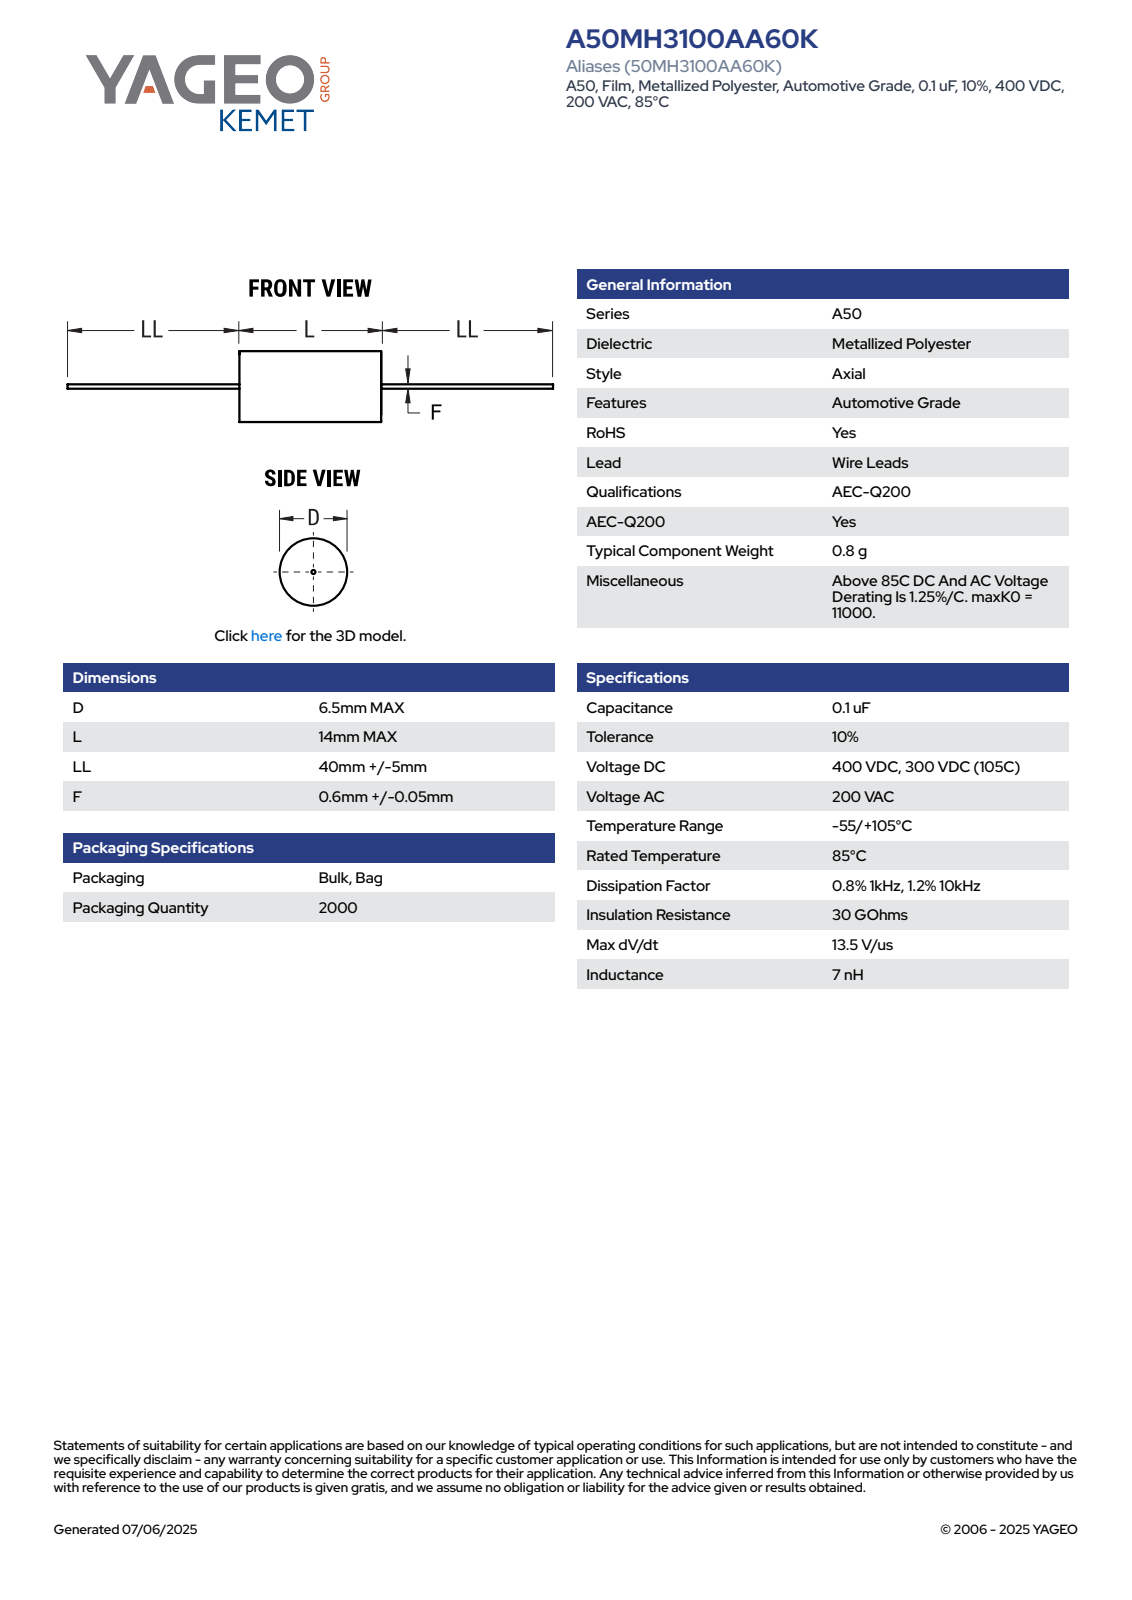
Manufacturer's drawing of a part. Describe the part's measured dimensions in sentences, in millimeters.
The part is named "CFA_ACWF_6.5X14_D6.5L14LL45F0.65". Its 3-D file was written by "SolidWorks 2014 (AUTOMOTIVE_DESIGN)". It is 1 solid with 72 faces: 26 planar, 15 cylindrical and 31 other. Overall it measures 104 by 6.51 by 6.5 millimeters. Its volume is 495 cubic millimeters and its surface area 537 square millimeters. Round bosses or shafts: 1 of diameter 6.5, 1 of diameter 0.65. Partial cylindrical surfaces (rounded edges, fillets, slot ends): 1 of radius 3.26. The main face-to-face distances are 14, 45, 59, 104.
